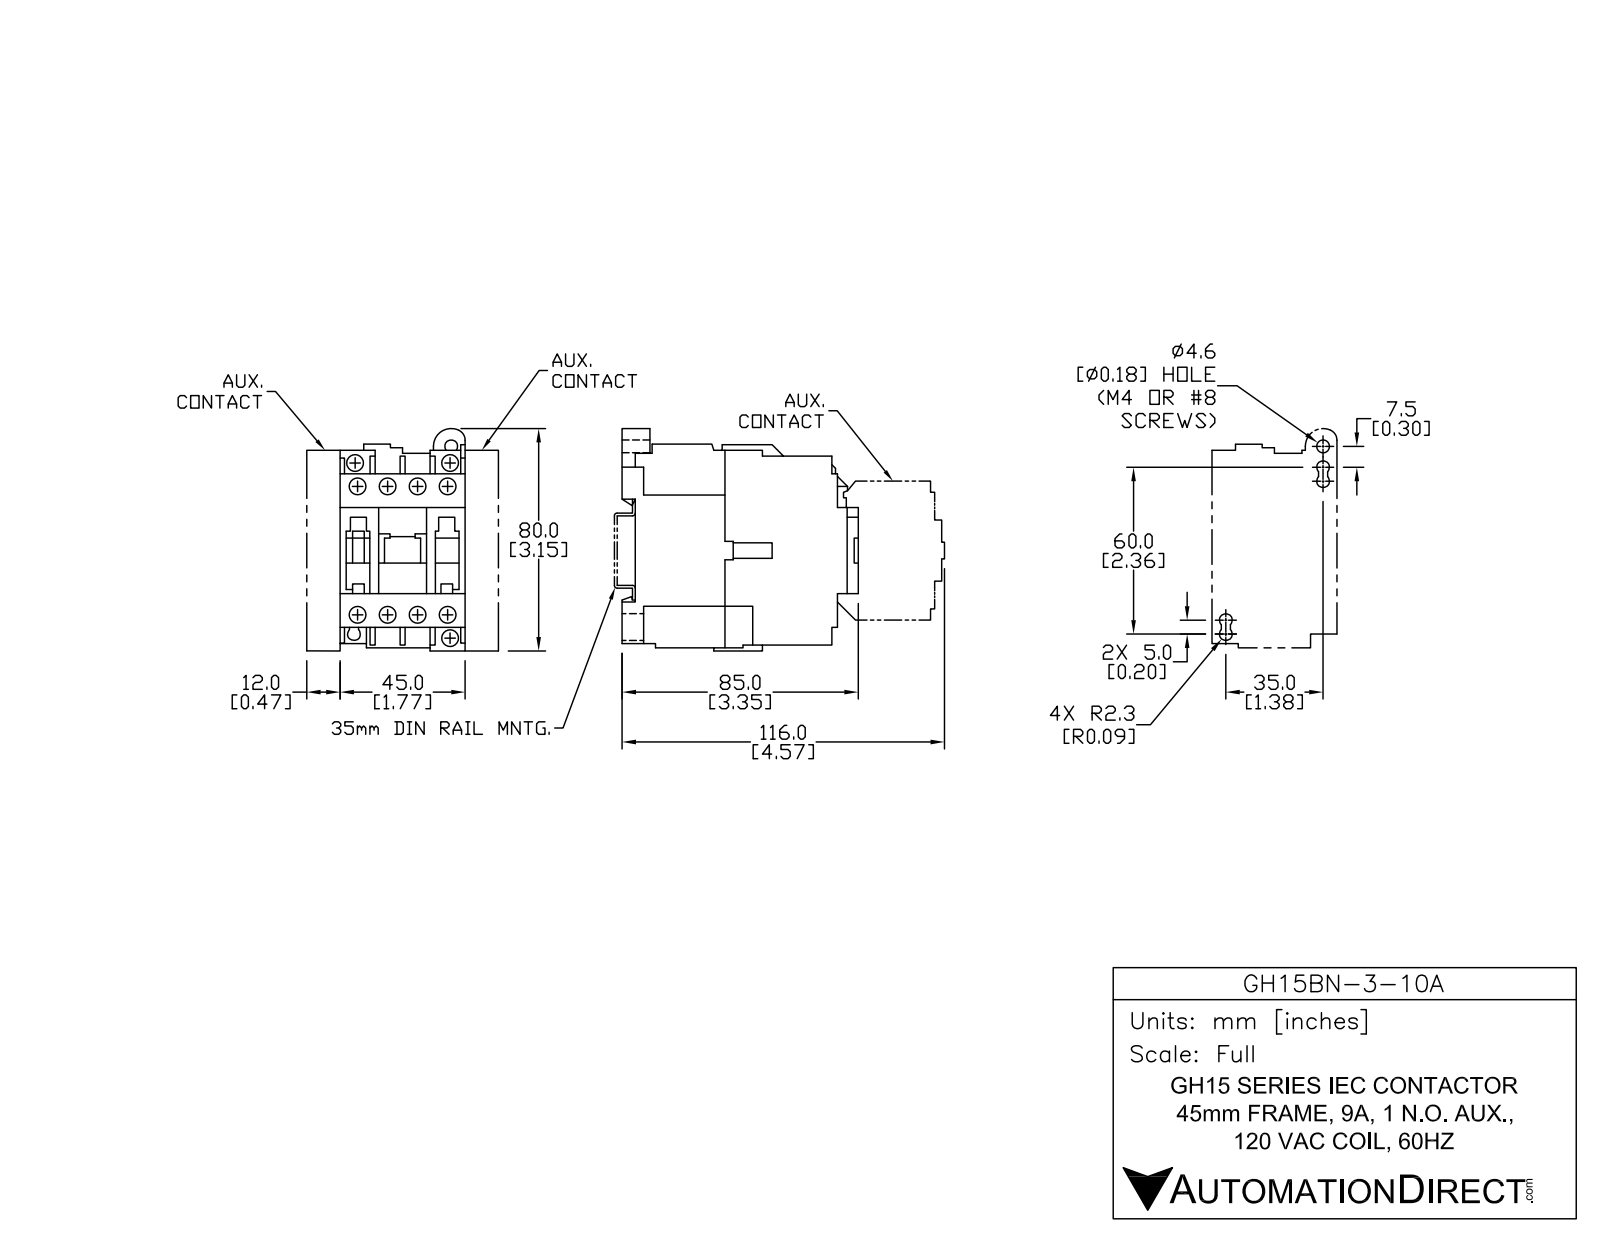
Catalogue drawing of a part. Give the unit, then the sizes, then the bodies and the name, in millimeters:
Units: millimetres
Overall size (bounding box): 85.5 × 80 × 45
Round holes (diameter × count): ⌀6.25 ×9, ⌀6.5 ×2, ⌀4.6 ×1
Partial cylindrical surfaces — rounded edges, fillets, slot ends (radius × count): R1 ×10, R2.3 ×8, R4.75 ×8, R3 ×2, R4.99 ×1, R5 ×1
Main face-to-face distances: 45, 9.5, 35.5, 12.12, 23.38, 8, 7, 33.75, 10.38, 32.87
Hole centre spacings: 11.25, 47.12, 22.5, 45.76, 50.99, 7.62, 33.75, 53.38
Volume: 196 351 mm³ · Surface area: 35 792 mm²
Bodies: 1 solid, 672 faces (451 planar, 65 cylindrical, 156 other)
Part name (STEP PRODUCT): GH15BN-3-10A
STEP written by: SolidWorks 2009 (AUTOMOTIVE_DESIGN)
